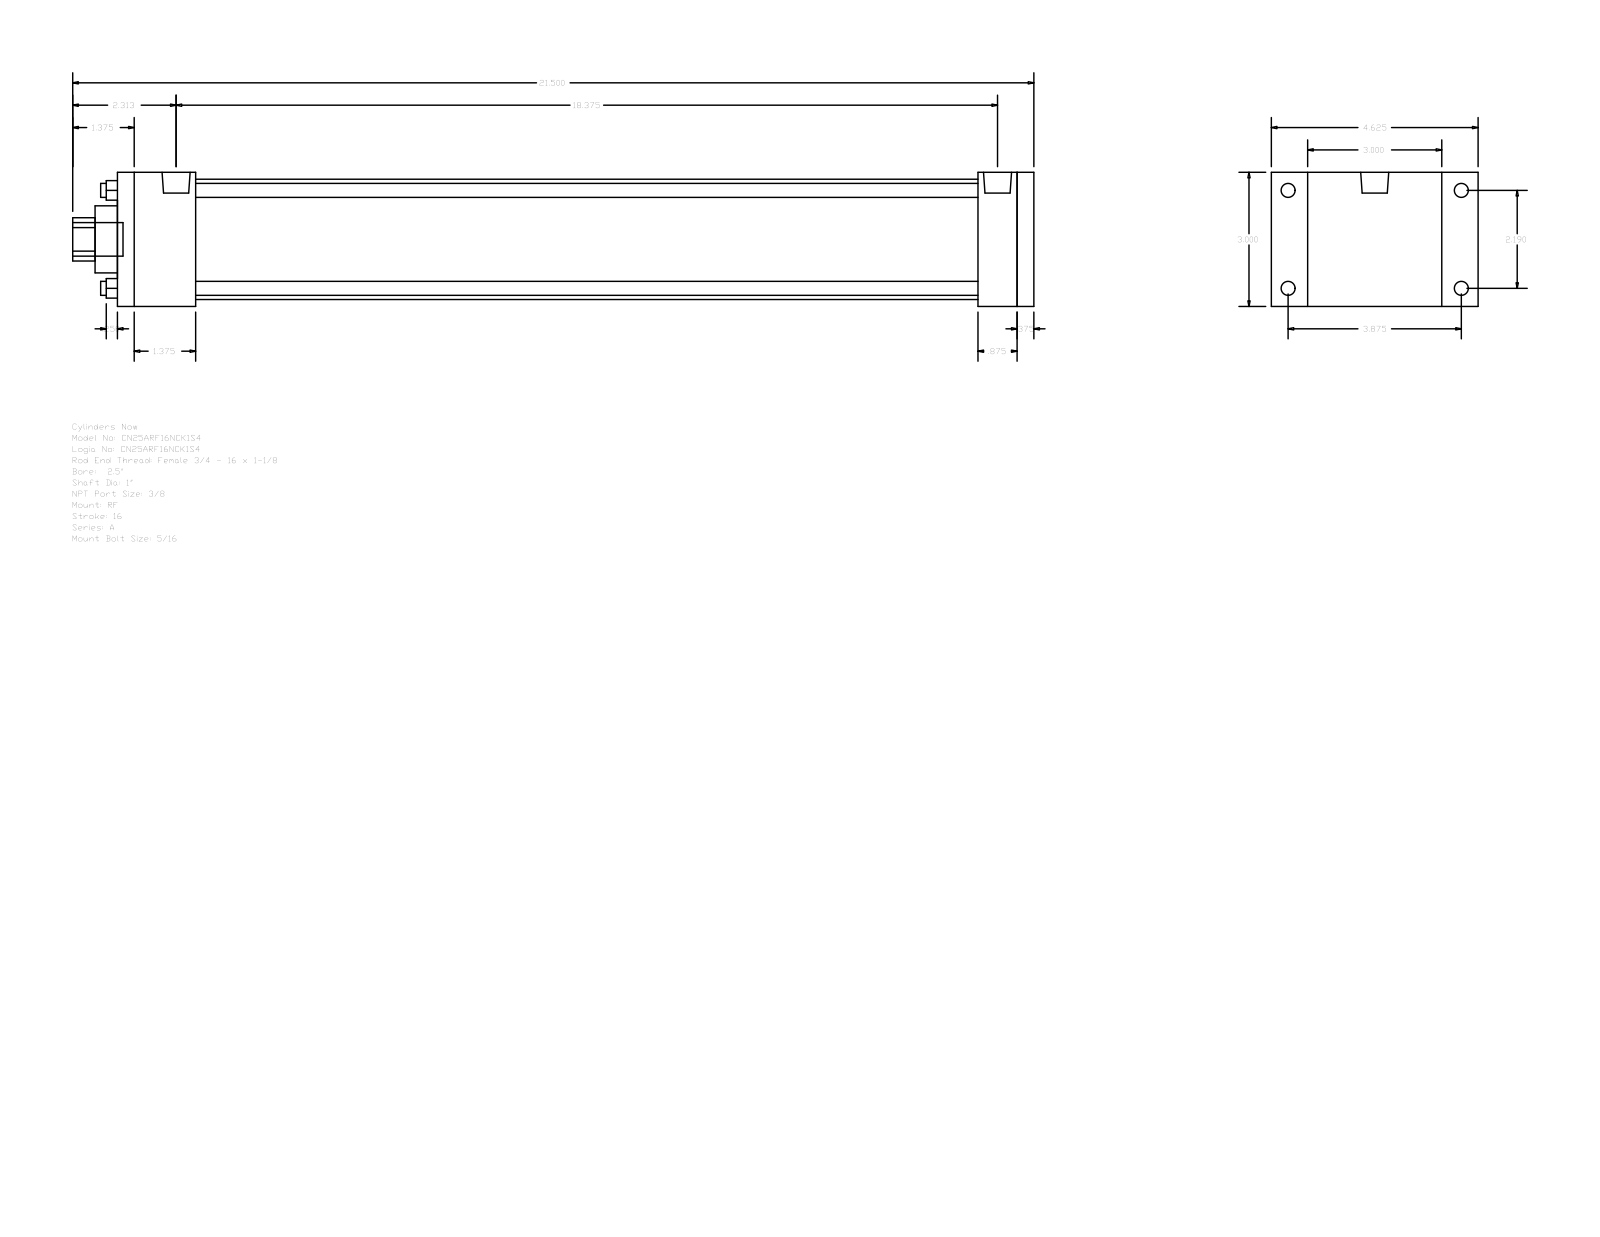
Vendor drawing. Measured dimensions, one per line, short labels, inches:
name: A_RF__0250_1
written by: GSSL Pune (CONFIG_CONTROL_DESIGN)
unit: in
bodies: 0 solids, 92 faces (64 planar, 28 cylindrical, 0 other)
size: 21.5 × 4.625 × 3
holes: 4× ⌀0.313, 1× ⌀1, 1× ⌀1.5, 1× ⌀2.69
bosses: 4× ⌀0.313, 4× ⌀0.219, 2× ⌀0.627, 1× ⌀0.75
rounds: 1× R0.484
face distances: 3, 20.5, 0.375, 20.125, 1.75, 19.25, 17.5, 18.375, 18.75, 0.875
hole spacings: 1.548, 2.19, 3.097
